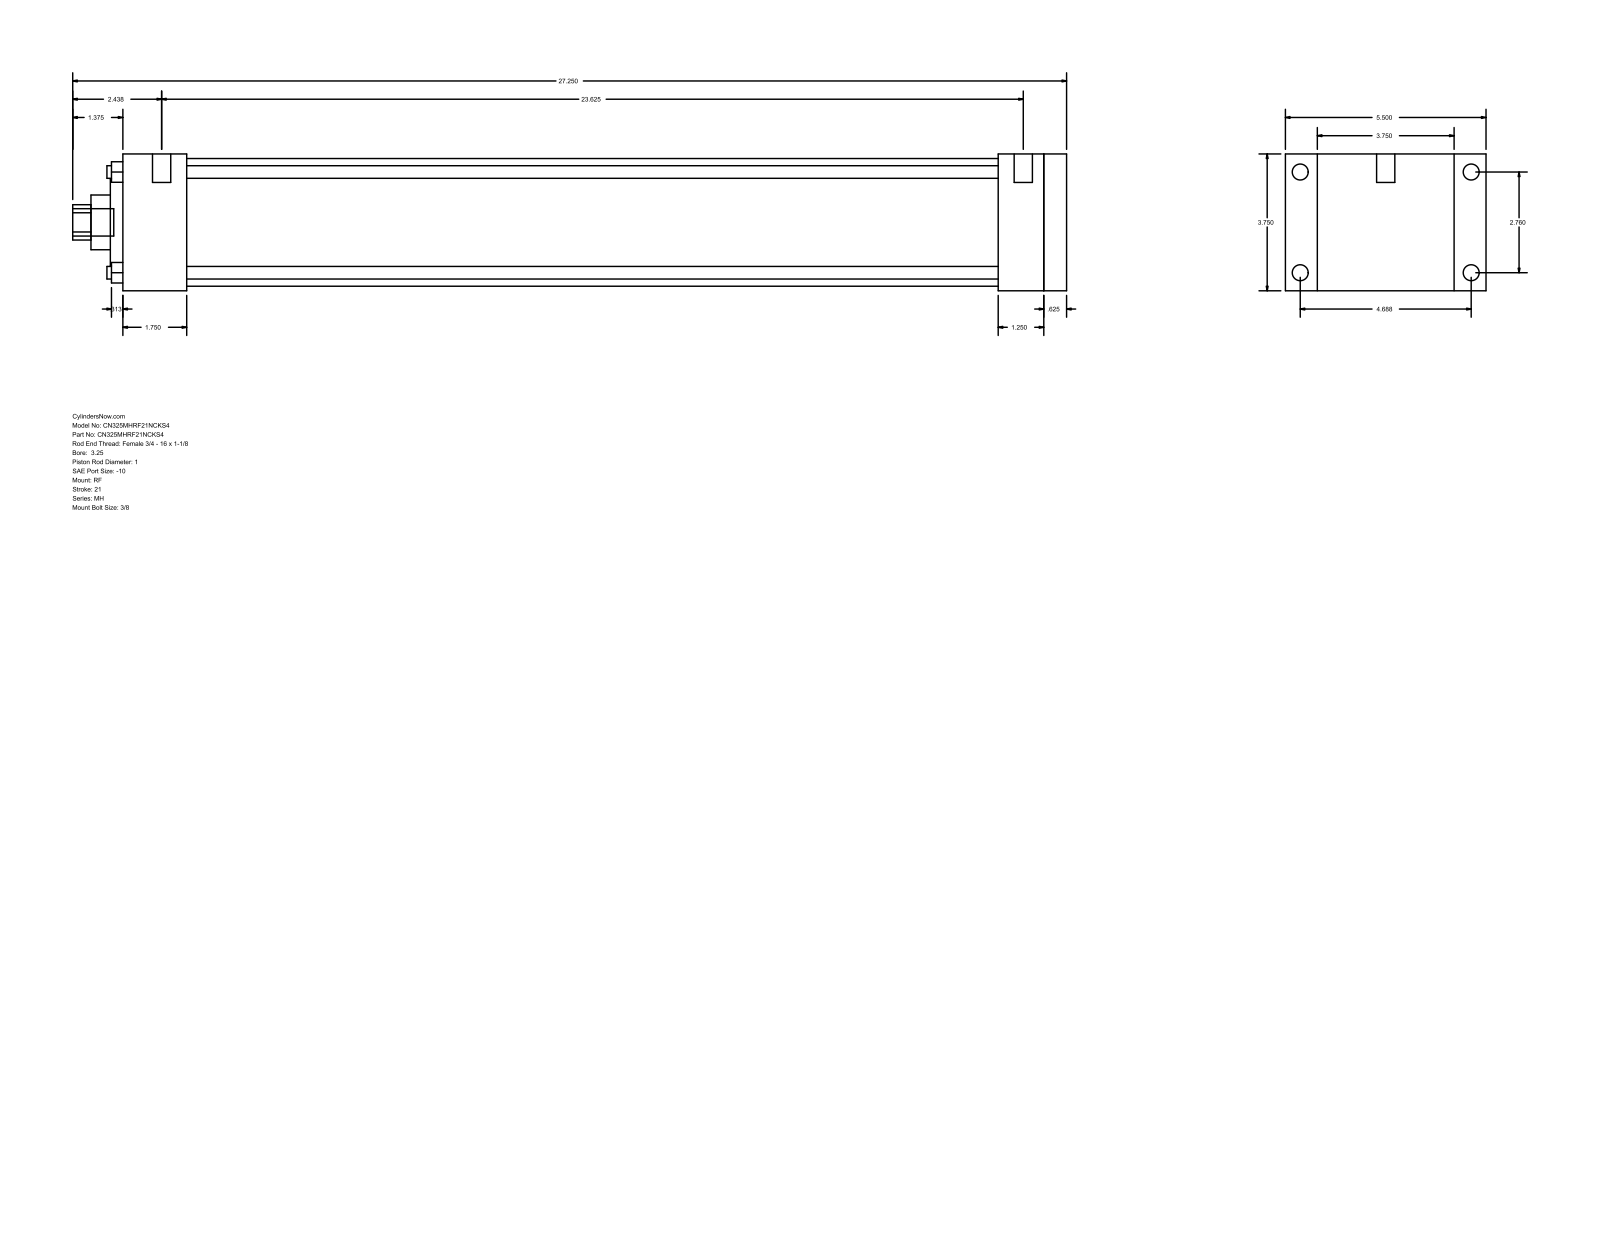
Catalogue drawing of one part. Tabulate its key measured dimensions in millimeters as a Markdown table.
| quantity | value |
| --- | --- |
| part name | MH_RF__0325_1 |
| STEP written by | GSSL Pune (CONFIG_CONTROL_DESIGN) |
| units | millimeters |
| bodies | 0 solids, 94 faces (65 planar, 29 cylindrical, 0 other) |
| overall size | 692.15 × 139.7 × 95.25 |
| round holes (diameter × count) | 8.76 × 4, 25.4 × 1, 38.1 × 1, 60.33 × 1, 88.9 × 1 |
| round bosses / shafts (diameter × count) | 11.13 × 4, 5.56 × 4, 12.7 × 2, 19.05 × 1 |
| partial cylindrical surfaces (radius × count) | 12.29 × 1 |
| main face-to-face distances | 95.24, 657.23, 641.35, 15.88, 22.23, 117.47, 44.46, 596.89, 612.77, 609.6 |
| hole center spacings | 49.57, 70.1, 99.14 |
